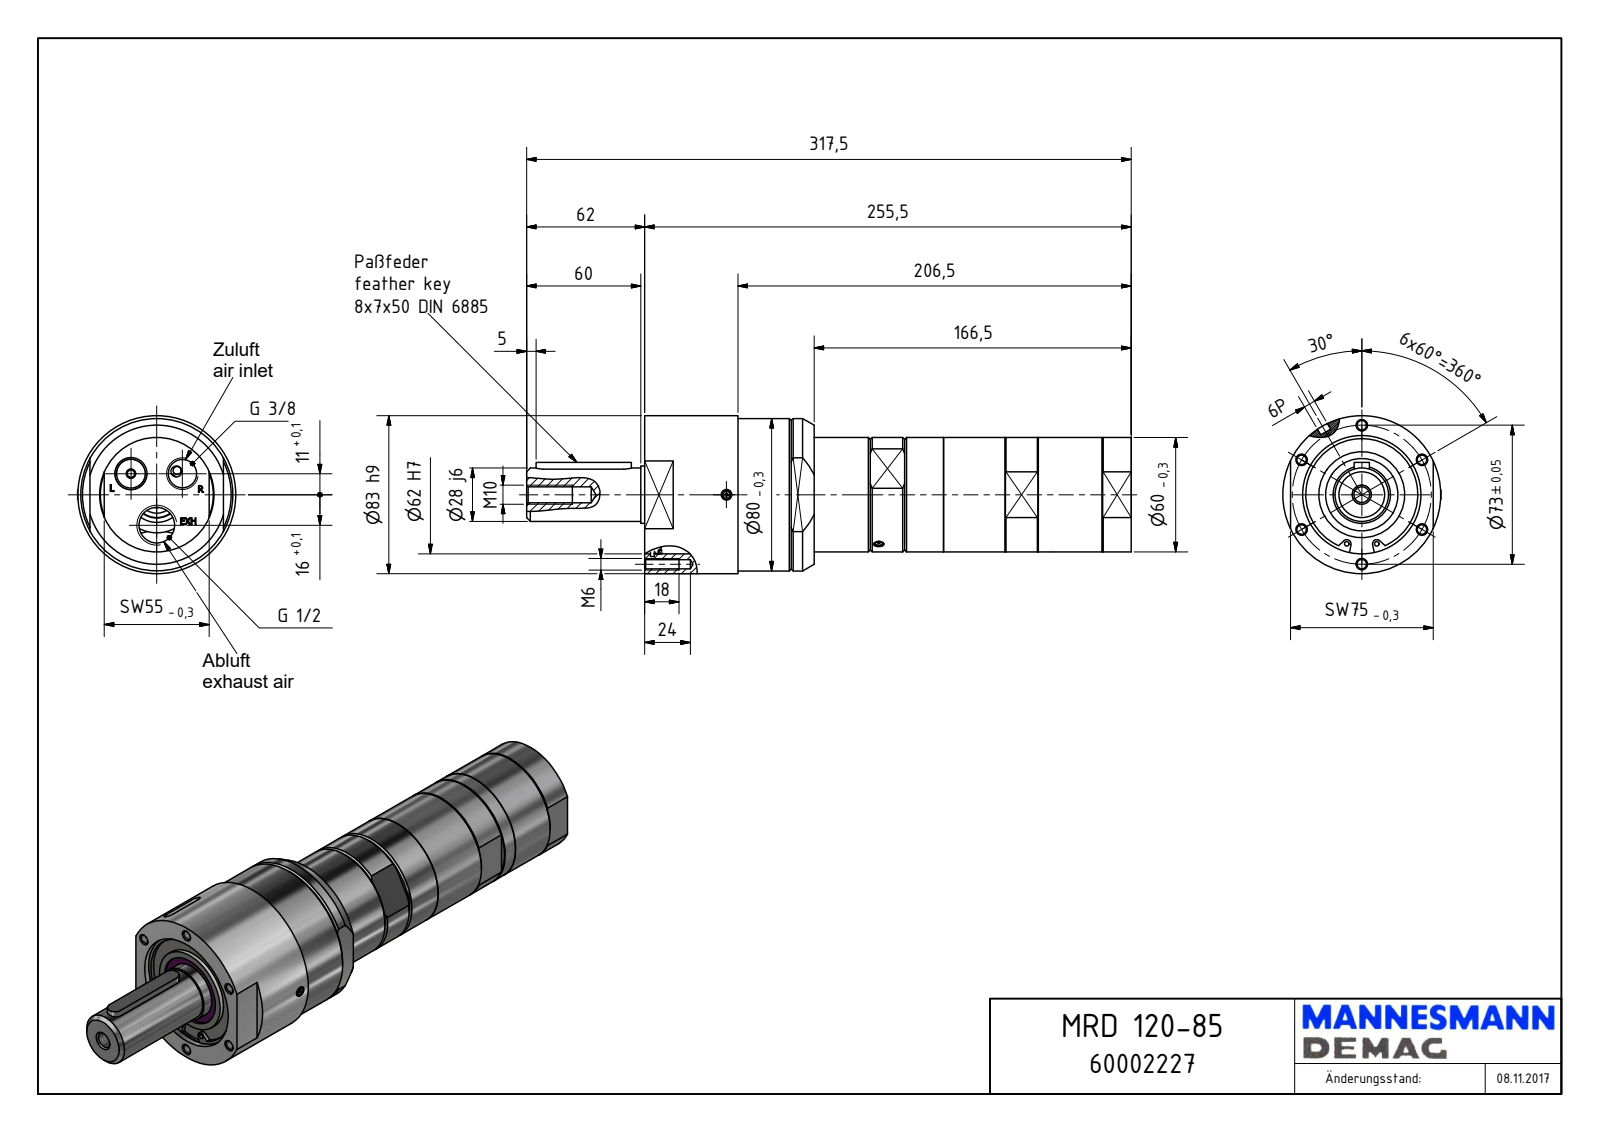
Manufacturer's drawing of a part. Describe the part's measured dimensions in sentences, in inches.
The part is named "MRD 120-85_60002227". Its 3-D file was written by "Autodesk Inventor 2018 (AUTOMOTIVE_DESIGN)". It is 1 solid with 623 faces: 252 planar, 293 cylindrical and 78 other. Overall it measures 12.5 by 3.268 by 3.268 inches. Its volume is 57.09 cubic inches and its surface area 141.8 square inches. Round holes: 6 of diameter 0.194, 3 of diameter 0.157, 2 of diameter 0.061, 2 of diameter 0.098, 2 of diameter 0.217, 2 of diameter 0.589, 1 of diameter 0.33, 1 of diameter 0.733, 1 of diameter 1.437, 1 of diameter 1.496, 1 of diameter 1.575, 1 of diameter 2.102. Round bosses or shafts: 2 of diameter 0.197, 2 of diameter 0.142, 1 of diameter 3.268, 1 of diameter 3.15, 1 of diameter 2.684, 1 of diameter 2.638, 1 of diameter 2.362, 1 of diameter 2.094. Partial cylindrical surfaces (rounded edges, fillets, slot ends): 94 of radius 0.138, 4 of radius 0.308, 2 of radius 0.089, 2 of radius 0.118, 2 of radius 0.157, 2 of radius 0.295, 2 of radius 0.398, 1 of radius 0.335. The main face-to-face distances are 10.059, 0.098, 6.555, 2.559, 3.504, 0.197, 3.307, 9.862, 0.394, 2.165. The hole center spacings are 1.437, 2.489, 2.874, 0.495, 0.523, 0.685, 0.768, 0.98.
